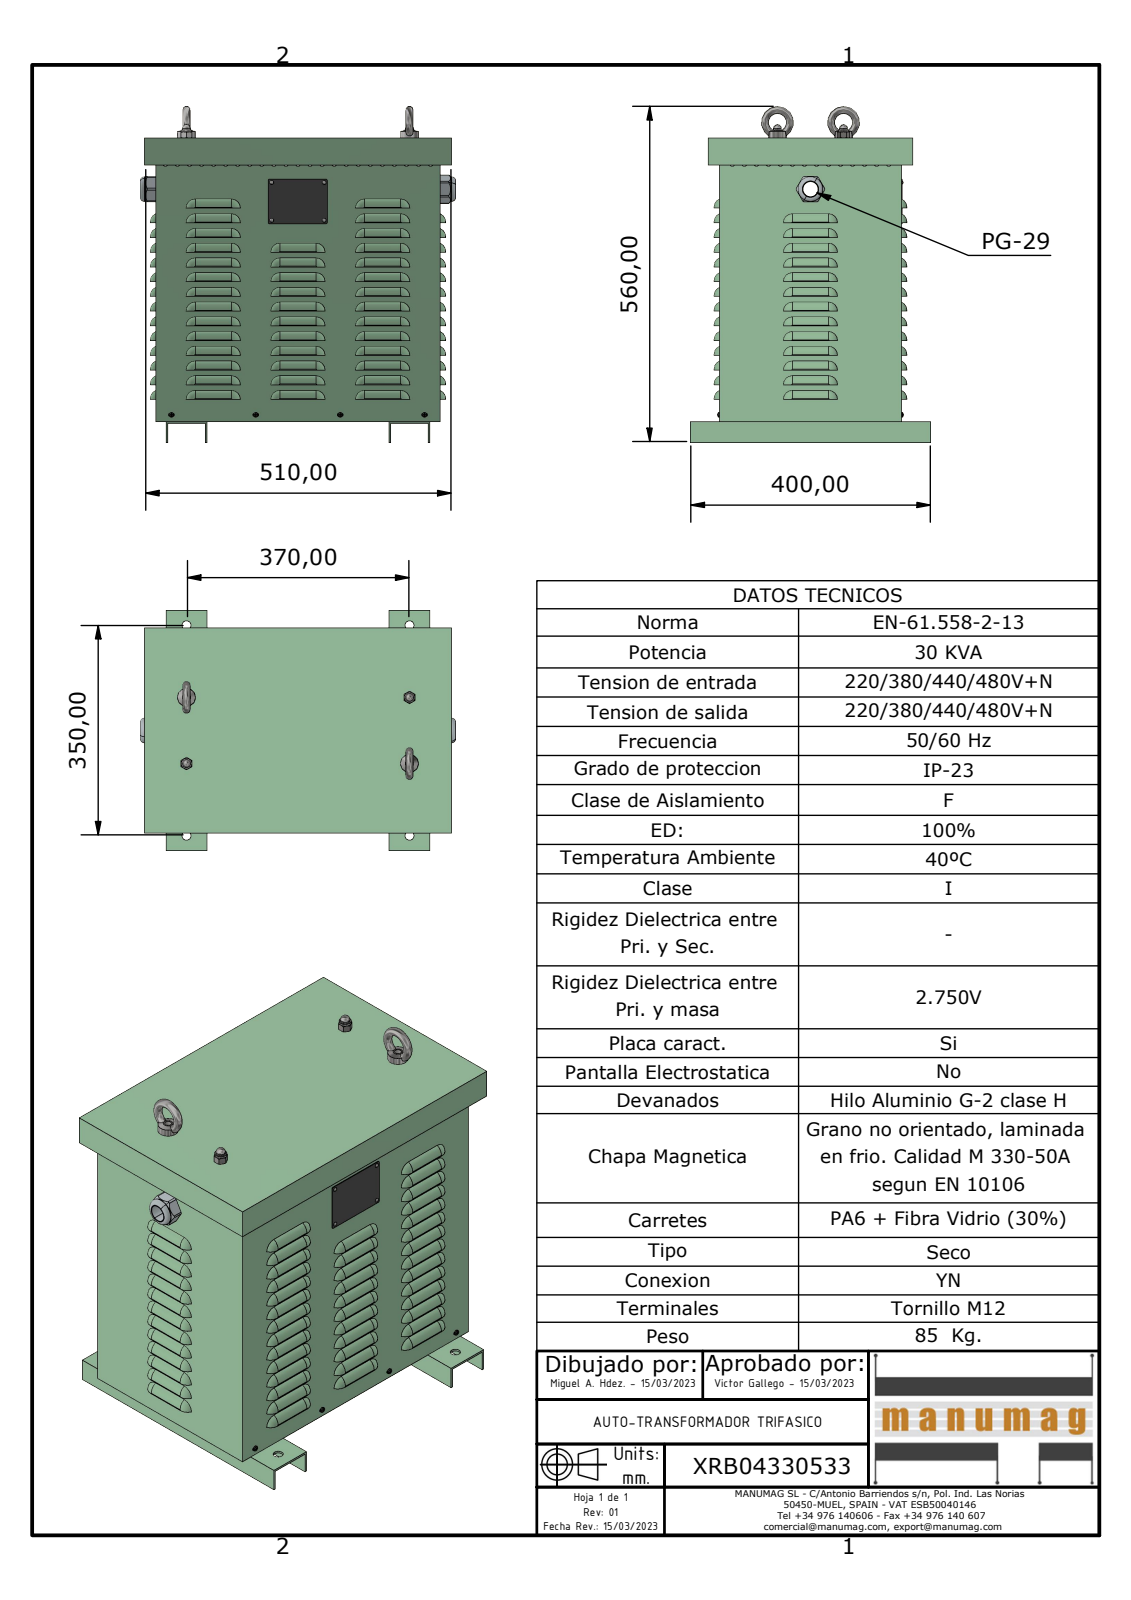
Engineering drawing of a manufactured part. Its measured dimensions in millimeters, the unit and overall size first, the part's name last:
Units: millimetres
Overall size (bounding box): 560 × 523.4 × 400
Round holes (diameter × count): ⌀11 ×260, ⌀15 ×8, ⌀4 ×4, ⌀5 ×4, ⌀10.11 ×4, ⌀14 ×4, ⌀25 ×1, ⌀38 ×1
Round bosses / shafts (diameter × count): ⌀4 ×4, ⌀3.62 ×4, ⌀3.2 ×4, ⌀30 ×2, ⌀18 ×2, ⌀13.6 ×2, ⌀40.8 ×1, ⌀37.3 ×1
Partial cylindrical surfaces — rounded edges, fillets, slot ends (radius × count): R14 ×104, R5 ×74, R7 ×54, R15 ×54, R3.22 ×12, R2.5 ×8, R2 ×4, R23.85 ×1
Main face-to-face distances: 2, 470, 301, 472, 468, 299, 303, 19, 3, 21
Hole centre spacings: 31.76, 71.59, 15, 28, 70, 44.6, 99.14, 140.8
Volume: 2 982 000 mm³ · Surface area: 2 640 000 mm²
Bodies: 24 solids, 2363 faces (789 planar, 948 cylindrical, 626 other)
Part name (STEP PRODUCT): XRB04330533; JE030 CUERPO; JE030 BASE; JE030 PATAS (+7 more)
STEP written by: Autodesk Inventor 2023 (AUTOMOTIVE_DESIGN)
